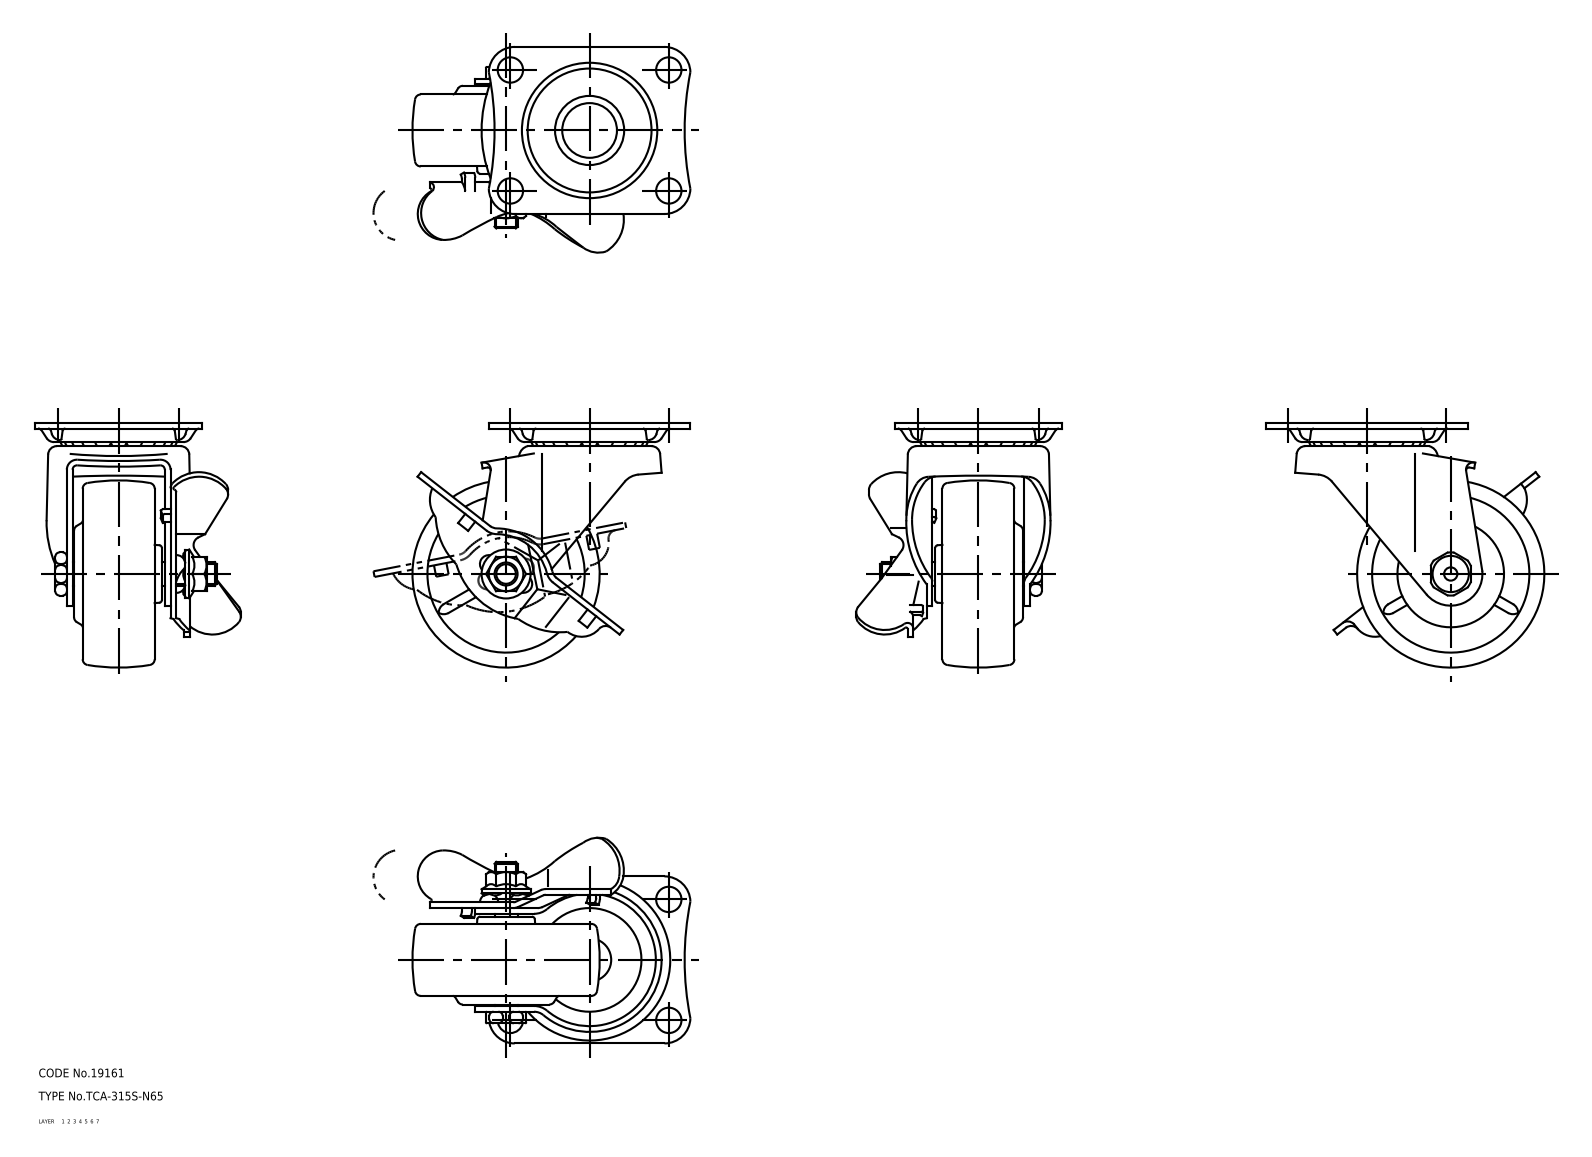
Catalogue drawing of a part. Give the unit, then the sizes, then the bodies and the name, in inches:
Units: inches
Overall size (bounding box): 3.799 × 3.346 × 2.811
Volume: 6.169 in³ · Surface area: 79.38 in²
Bodies: 6 solids, 609 faces (0 planar, 0 cylindrical, 609 other)
Part name (STEP PRODUCT): wheel; mounting plate; main shaft; lever (+2 more)
STEP written by: CADfix (AUTOMOTIVE_DESIGN)
